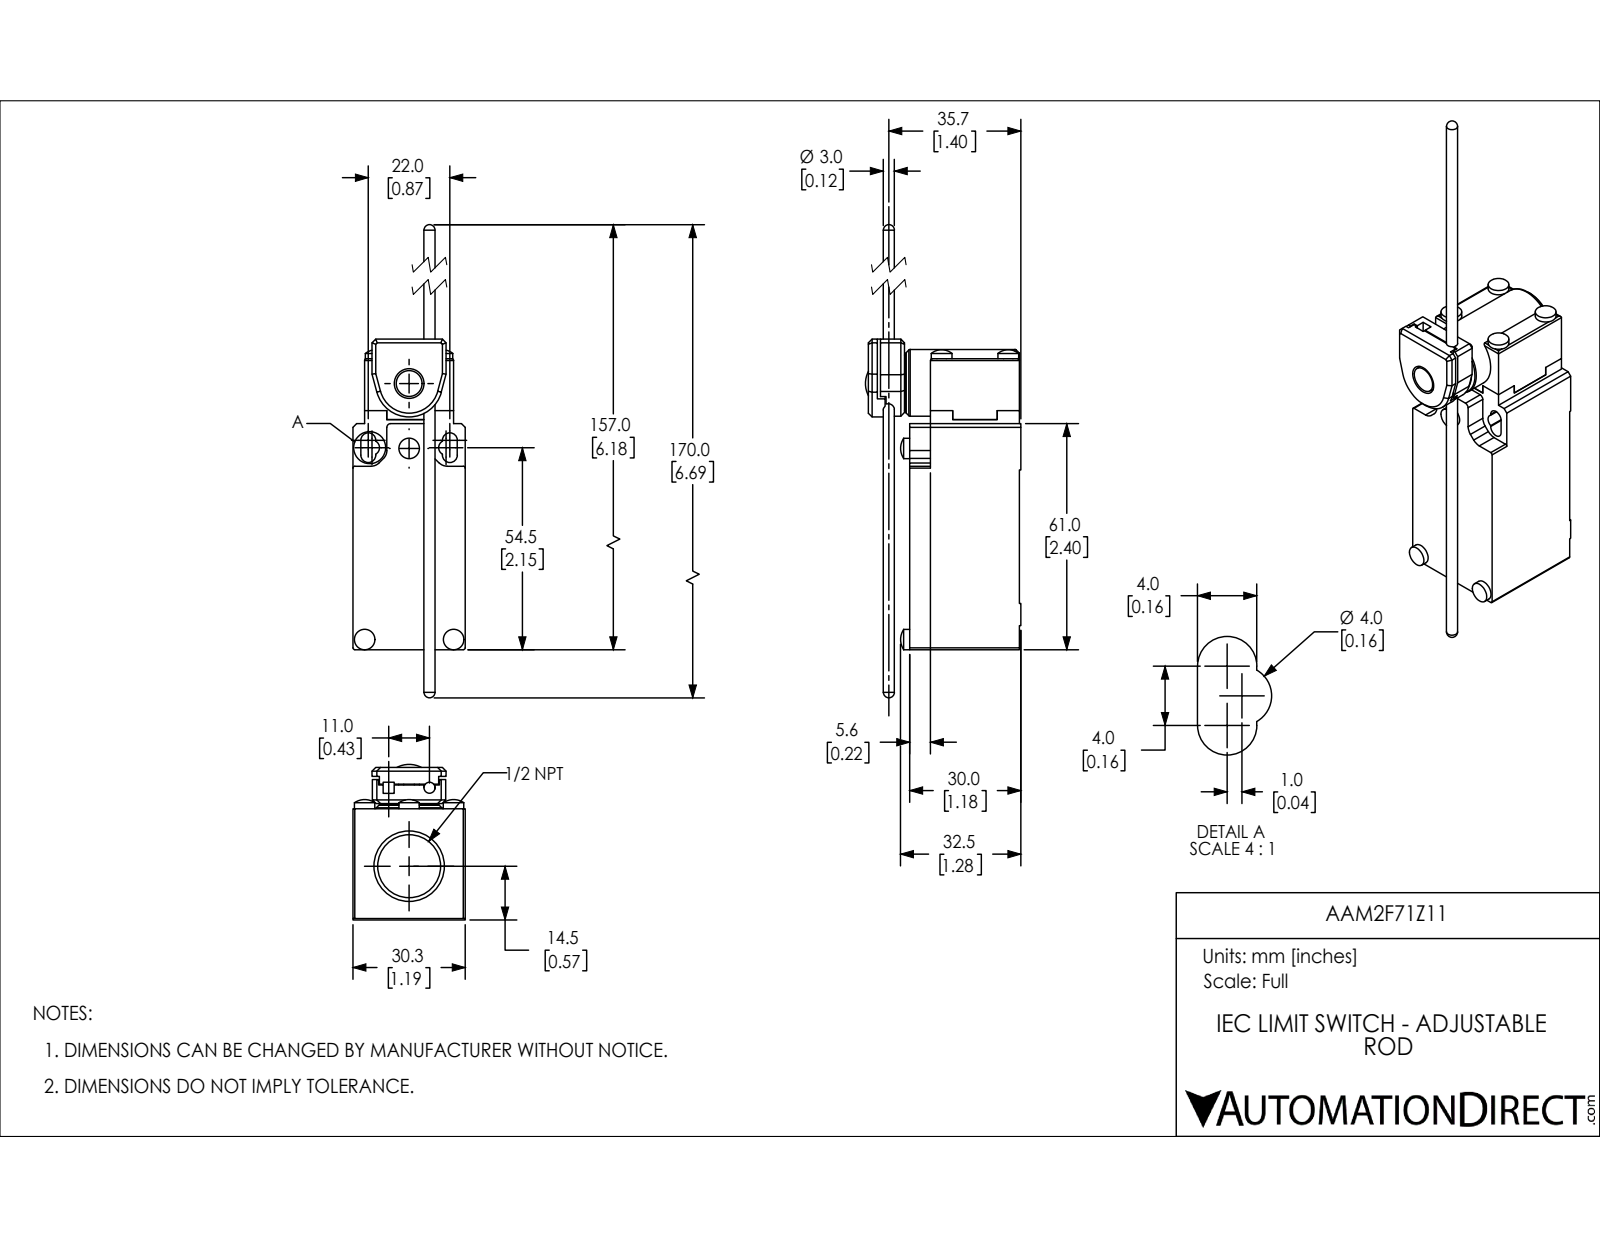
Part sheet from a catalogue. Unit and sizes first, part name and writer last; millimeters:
Units: millimetres
Overall size (bounding box): 170 × 42 × 30.3
Round holes (diameter × count): ⌀3 ×1, ⌀8 ×1, ⌀11 ×1, ⌀17 ×1, ⌀19 ×1
Round bosses / shafts (diameter × count): ⌀5.6 ×4, ⌀5.5 ×3, ⌀18 ×1, ⌀15 ×1, ⌀7 ×1
Partial cylindrical surfaces — rounded edges, fillets, slot ends (radius × count): R0.5 ×8, R2 ×6, R3 ×4, R1 ×2, R4.6 ×1, R6.4 ×1, R9 ×1, R10 ×1
Main face-to-face distances: 30.3, 29.6, 3.1, 27.2, 24, 30, 6, 0.4, 7, 62.1
Hole centre spacings: 21.8
Volume: 67 690 mm³ · Surface area: 18 010 mm²
Bodies: 4 solids, 273 faces (149 planar, 92 cylindrical, 32 other)
Part name (STEP PRODUCT): AAM2F71Z11
STEP written by: SolidWorks 2018 (AUTOMOTIVE_DESIGN)
